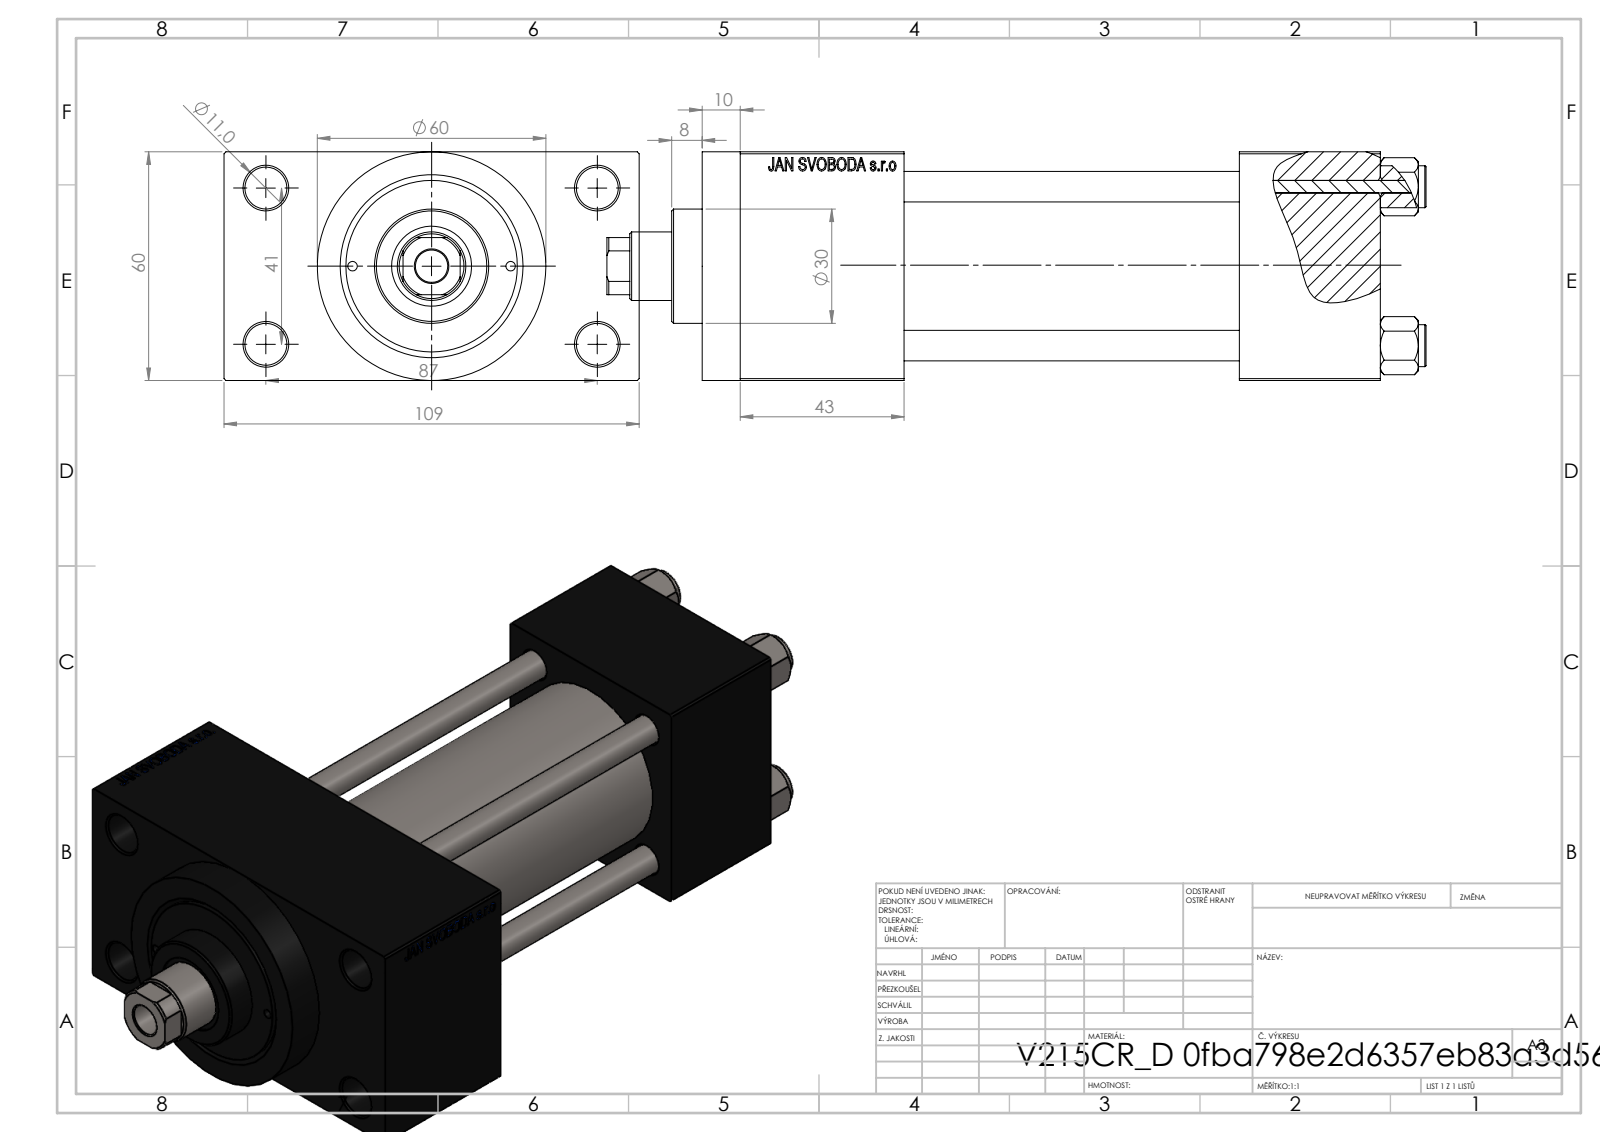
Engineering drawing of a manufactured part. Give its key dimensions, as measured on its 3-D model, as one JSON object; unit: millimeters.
{"part_name": "V215CR_D_TYCINKA; V215_VC_A; NUT_M5_D; V215CR_D_Body (+1 more)", "step_written_by": "SolidWorks 2019 (CONFIG_CONTROL_DESIGN)", "units": "millimeters", "bodies": {"solids": 11, "faces": 1112, "planar": 500, "cylindrical": 92, "other": 520}, "overall_size": [215, 109, 60], "volume_mm3": 538134, "surface_area_mm2": 135321, "round_holes": [[8, 4], [11, 4], [2.5, 2], [7, 2], [16.66, 2], [24, 2], [8.5, 1], [18, 1], [21, 1], [31, 1], [40, 1], [45, 1]], "round_bosses_or_shafts": [[11, 4], [60, 1], [46, 1], [30, 1]], "partial_cylinders_radius": [[8.5, 1]], "face_to_face_distances": [60, 88, 24.5, 84.5, 37, 125, 168, 131, 43, 134.74], "hole_center_spacings": [20.85, 22.65, 29.49, 30.62, 41.7, 46.53, 47.15, 48.09]}
